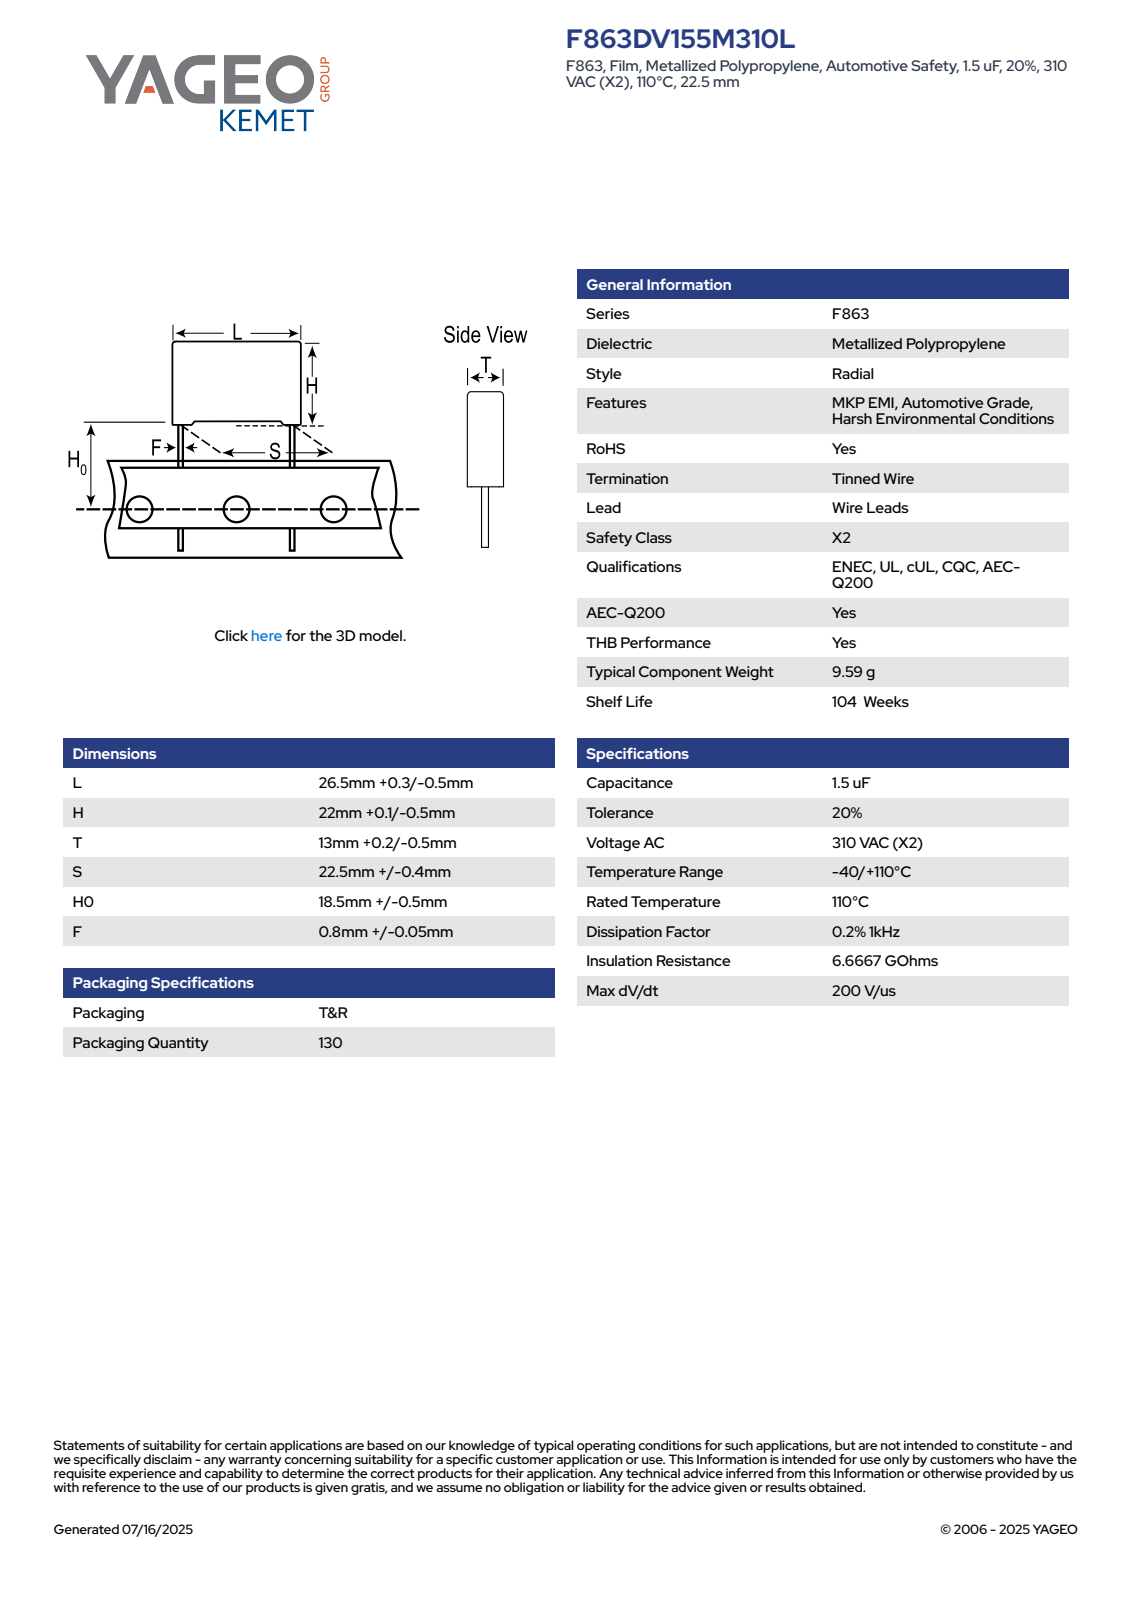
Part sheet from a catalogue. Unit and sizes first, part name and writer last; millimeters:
Units: millimetres
Overall size (bounding box): 41.1 × 26.8 × 13.21
Round bosses / shafts (diameter × count): ⌀0.85 ×2
Partial cylindrical surfaces — rounded edges, fillets, slot ends (radius × count): R0.5 ×4
Main face-to-face distances: 13.2, 26.8, 21.34, 21.35, 0.75, 0.76, 22.1, 0.89, 25.91, 13.21
Volume: 7 594 mm³ · Surface area: 2 617 mm²
Bodies: 4 solids, 85 faces (77 planar, 8 cylindrical, 0 other)
Part name (STEP PRODUCT): CFR_RB2_26.5X22X13_L26.8H22.1T13.2S22.5H019F0.85
STEP written by: SolidWorks 2020 (AUTOMOTIVE_DESIGN)
